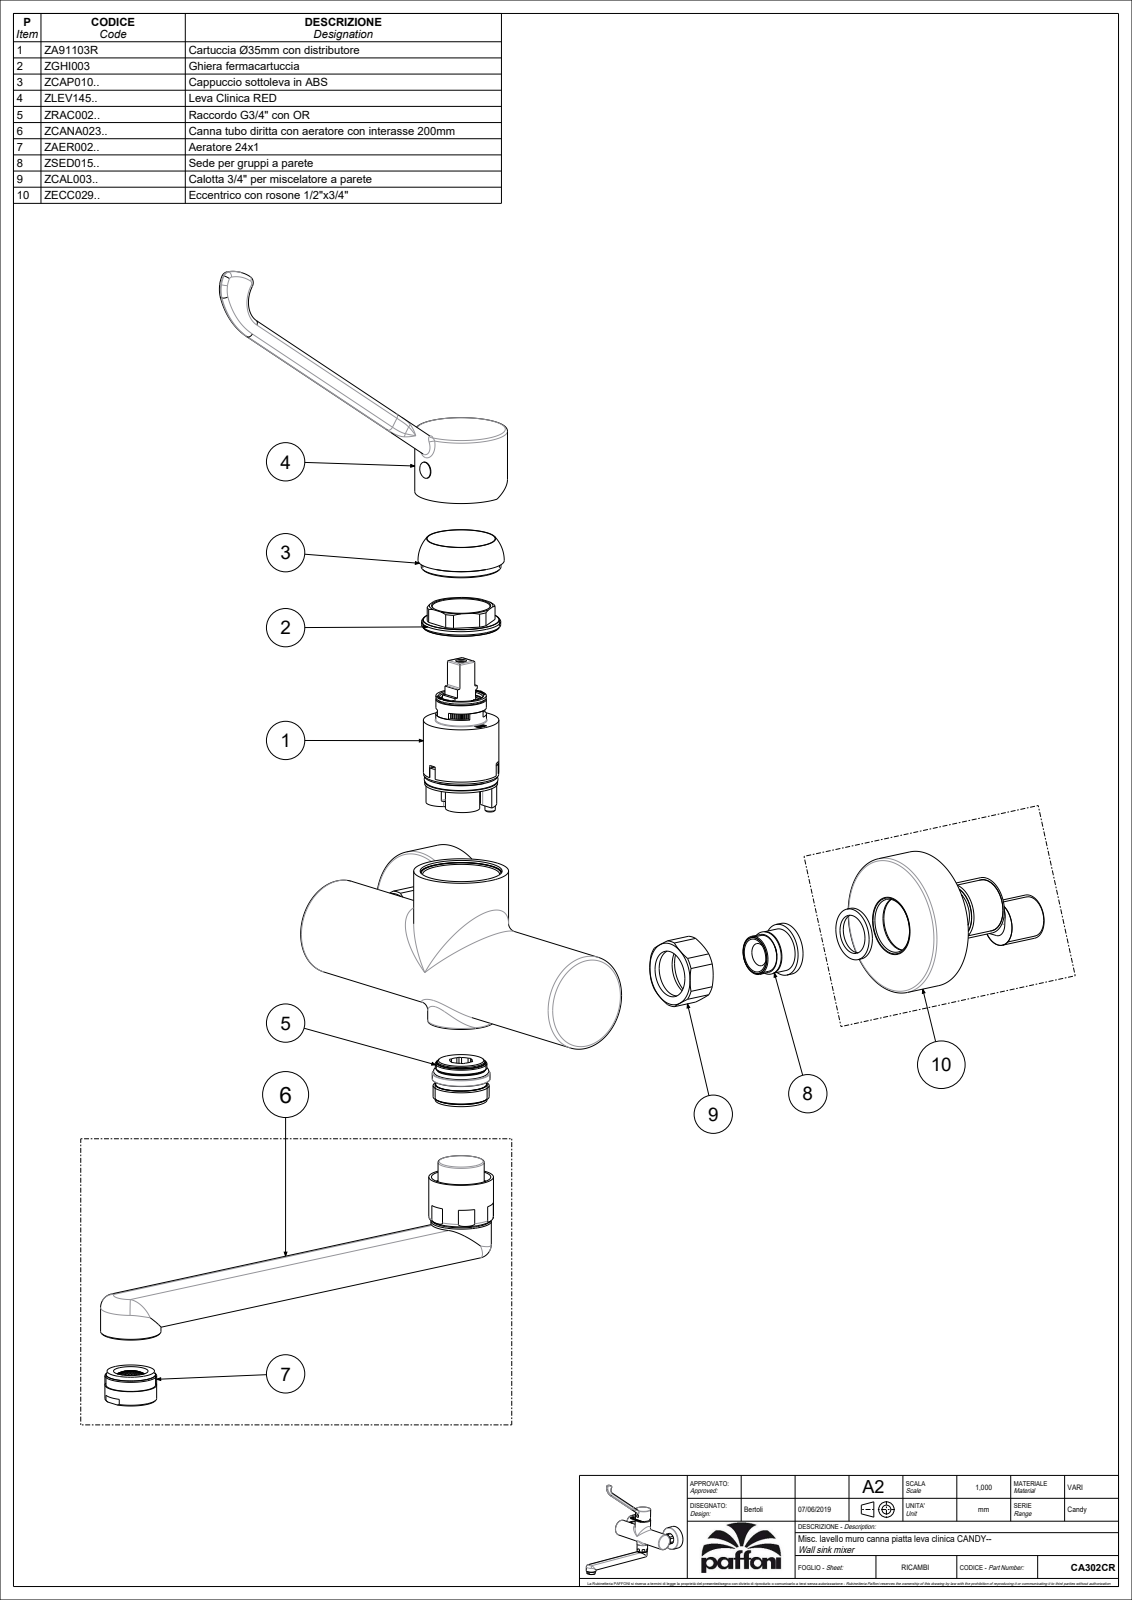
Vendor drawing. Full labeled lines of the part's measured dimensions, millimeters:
Part name (STEP PRODUCT): CA302CR
STEP written by: CREO PARAMETRIC BY PTC INC, 2020044 (CONFIG_CONTROL_DESIGN)
Units: millimetres
Bodies: 3 solids, 1299 faces (977 planar, 152 cylindrical, 170 other)
Overall size (bounding box): 271.5 × 251.58 × 213.5
Volume: 529 702 mm³ · Surface area: 110 382 mm²
Round holes (diameter × count): ⌀20.5 ×2, ⌀26 ×2, ⌀3 ×1, ⌀14.9 ×1, ⌀16.5 ×1, ⌀17 ×1, ⌀17.3 ×1, ⌀18.5 ×1, ⌀20 ×1, ⌀21 ×1, ⌀23 ×1, ⌀24.2 ×1
Round bosses / shafts (diameter × count): ⌀63.5 ×2, ⌀44 ×2, ⌀28 ×2, ⌀19.7 ×2, ⌀43 ×1, ⌀31 ×1, ⌀30 ×1, ⌀24 ×1
Partial cylindrical surfaces — rounded edges, fillets, slot ends (radius × count): R0.5 ×32, R2 ×4, R7 ×2, R8 ×2, R15.5 ×2, R18.3 ×2, R25.63 ×2, R3.5 ×1
Main face-to-face distances: 1, 15, 20, 14, 16, 4.5, 88.25, 92.75, 126.6, 127.6
Hole centre spacings: 96.86, 150, 200
